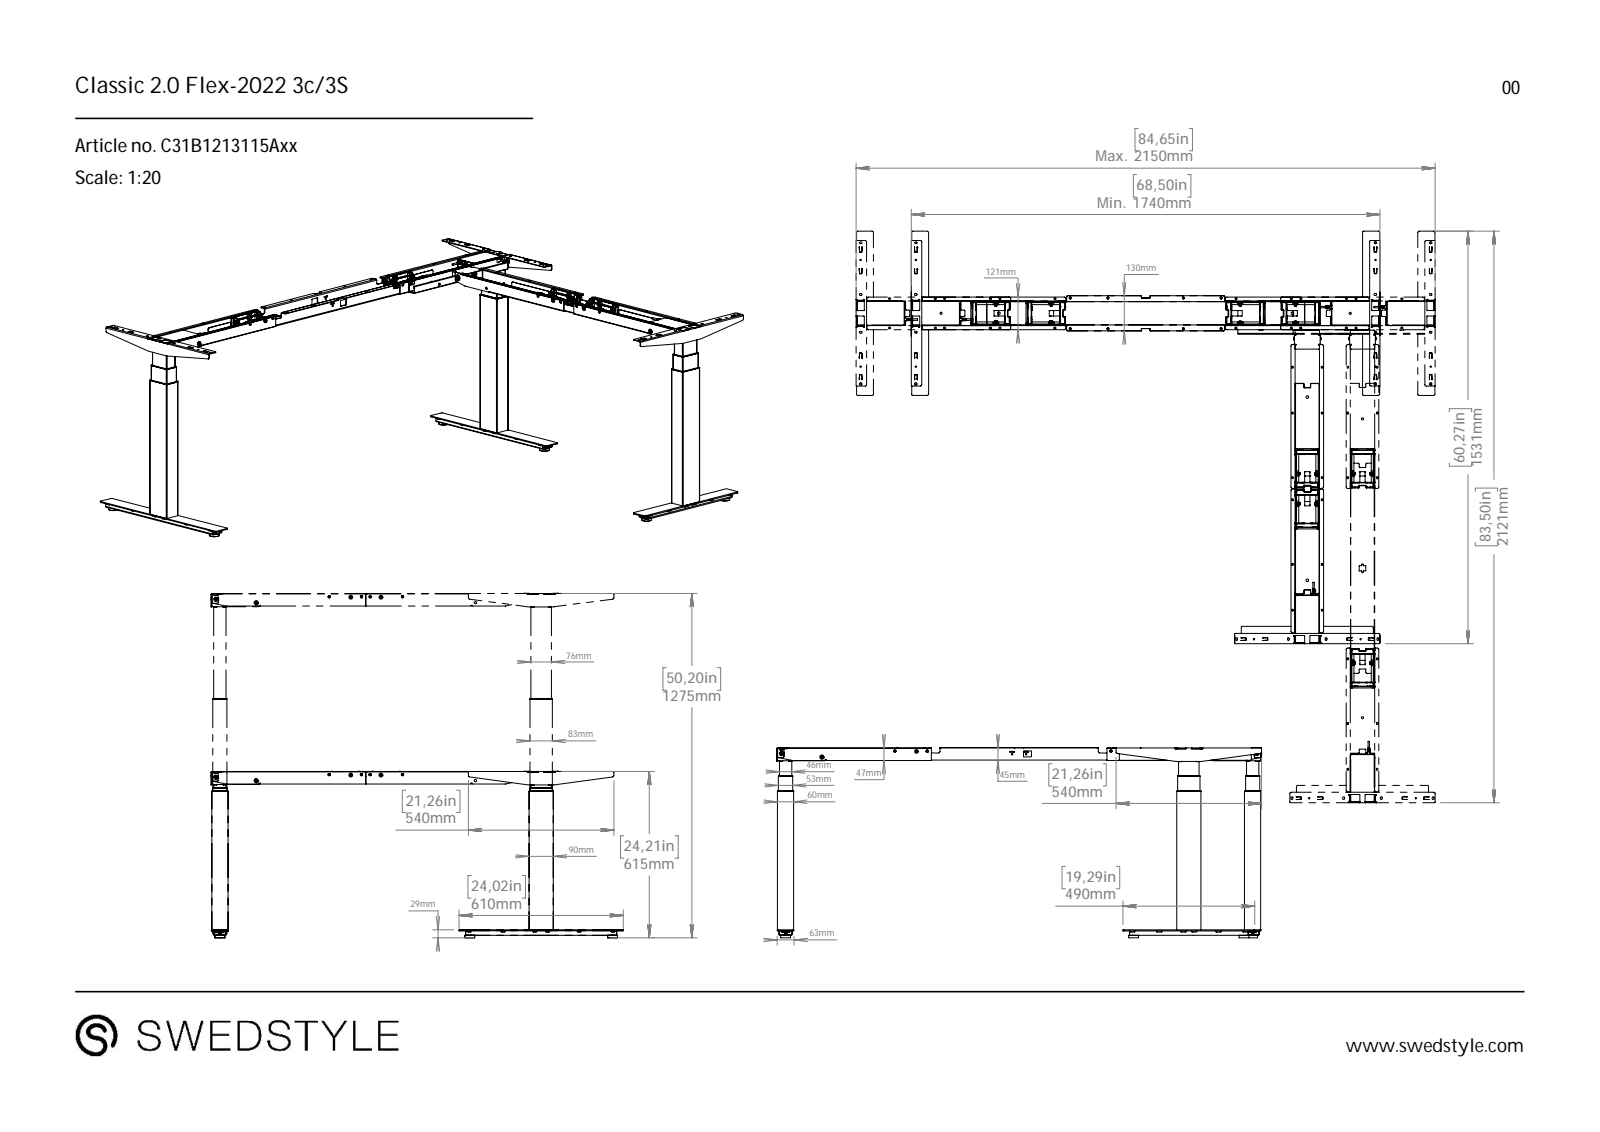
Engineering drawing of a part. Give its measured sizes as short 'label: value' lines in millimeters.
name: C31B1213115AxxG_ Classic 2.0 Flex -2023 3c_3S, Fl174_Fl115
written by: SolidWorks 2021 (CONFIG_CONTROL_DESIGN)
unit: mm
bodies: 0 solids, 3052 faces (1612 planar, 898 cylindrical, 542 other)
size: 1800 × 1580.88 × 706
holes: 15× ⌀8, 12× ⌀16, 8× ⌀7, 8× ⌀14, 6× ⌀8.6, 5× ⌀5, 4× ⌀10, 3× ⌀15.57, 2× ⌀5.4, 1× ⌀8.5
bosses: 4× ⌀8, 4× ⌀7.6, 3× ⌀15.57, 3× ⌀8.5, 3× ⌀5.5, 1× ⌀14
rounds: 128× R0.5, 120× R2.5, 45× R3, 34× R2.75, 28× R5, 27× R1, 26× R2, 26× R2.8
face distances: 3.5, 1.5, 2, 0.5, 53, 7, 3, 4, 1734, 49.5
hole spacings: 205.82, 240.32, 358.2, 549.88, 106.53, 114, 140, 180.54
